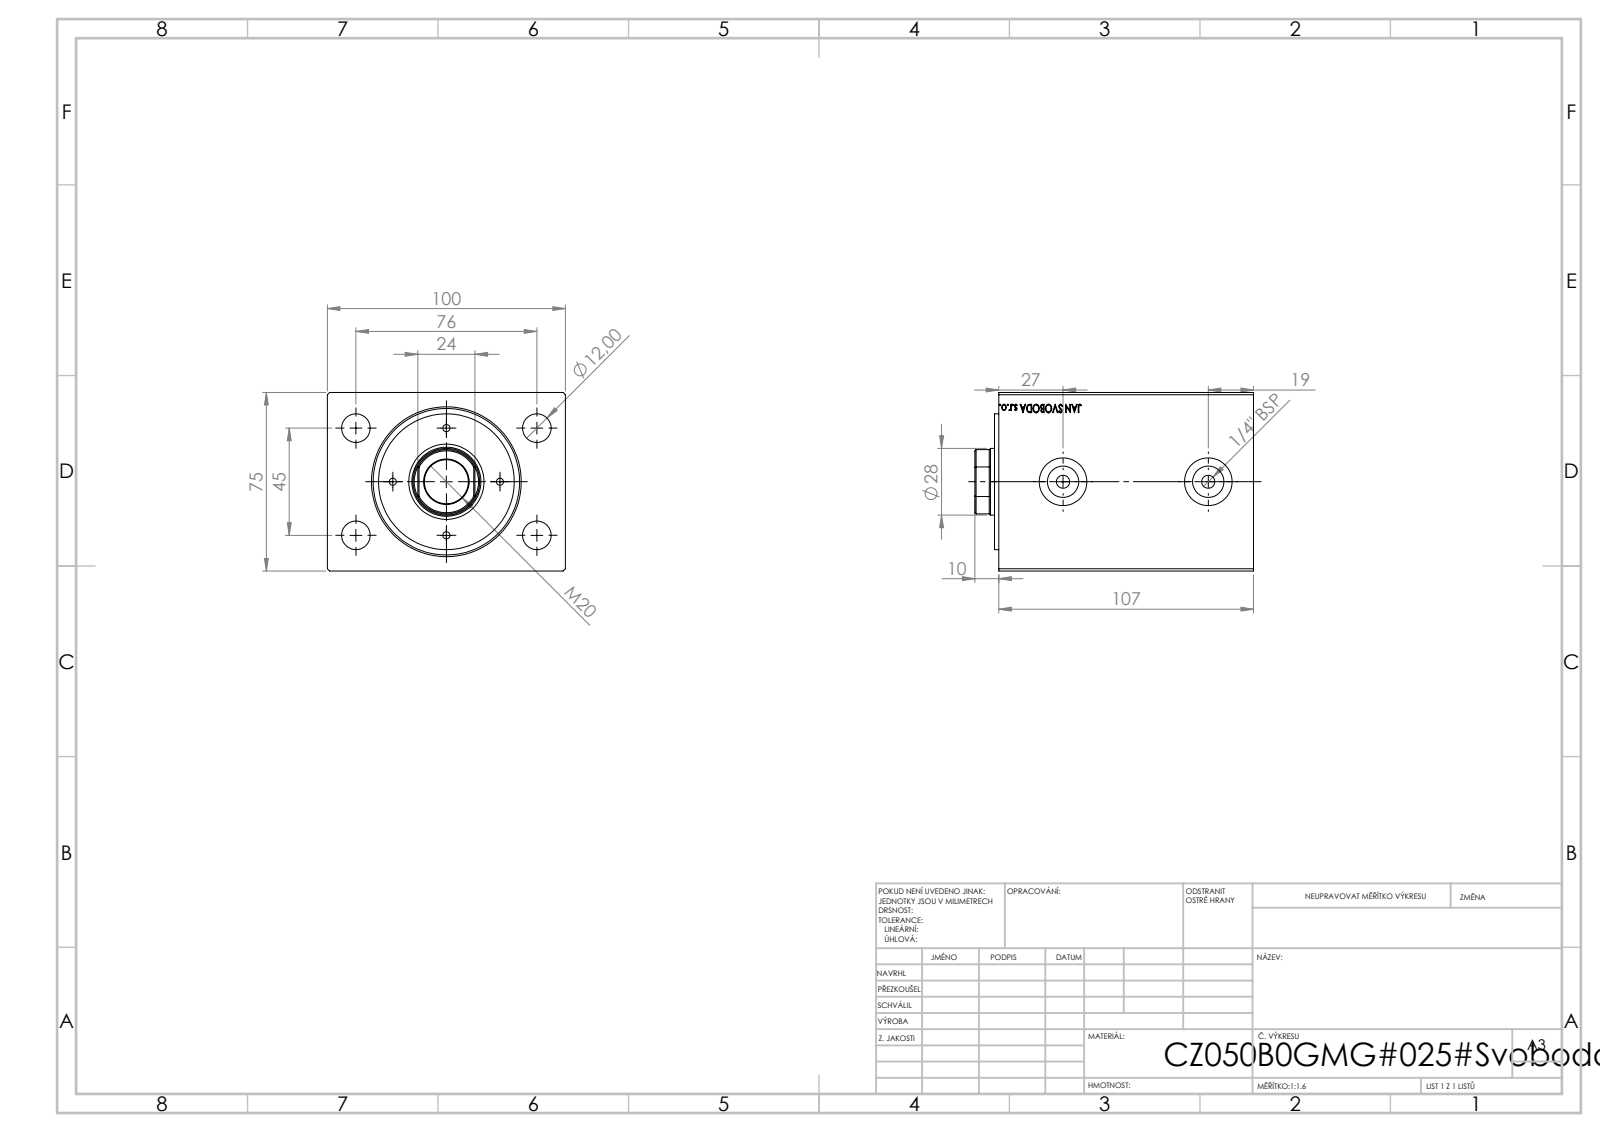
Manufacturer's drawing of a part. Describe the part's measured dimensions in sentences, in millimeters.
The part is named "V500CZ; V500CZ_B_VC". Its 3-D file was written by "SolidWorks 2019 (CONFIG_CONTROL_DESIGN)". It is 3 solids with 874 faces: 400 planar, 58 cylindrical and 416 other. Overall it measures 117 by 100 by 75 millimeters. Its volume is 737 436 cubic millimeters and its surface area 100 984 square millimeters. Round holes: 4 of diameter 3, 4 of diameter 12, 2 of diameter 5.5, 2 of diameter 13.16, 2 of diameter 20, 1 of diameter 18.5, 1 of diameter 28, 1 of diameter 29, 1 of diameter 36, 1 of diameter 50, 1 of diameter 61.5. Round bosses or shafts: 1 of diameter 57. Partial cylindrical surfaces (rounded edges, fillets, slot ends): 1 of radius 13.5. The main face-to-face distances are 75, 100, 107, 89.2, 17.8, 10, 1.8, 8.2, 81, 98.8. The hole center spacings are 22.5, 27.32, 31.82, 38, 44.16, 45, 58.9, 64.55.
